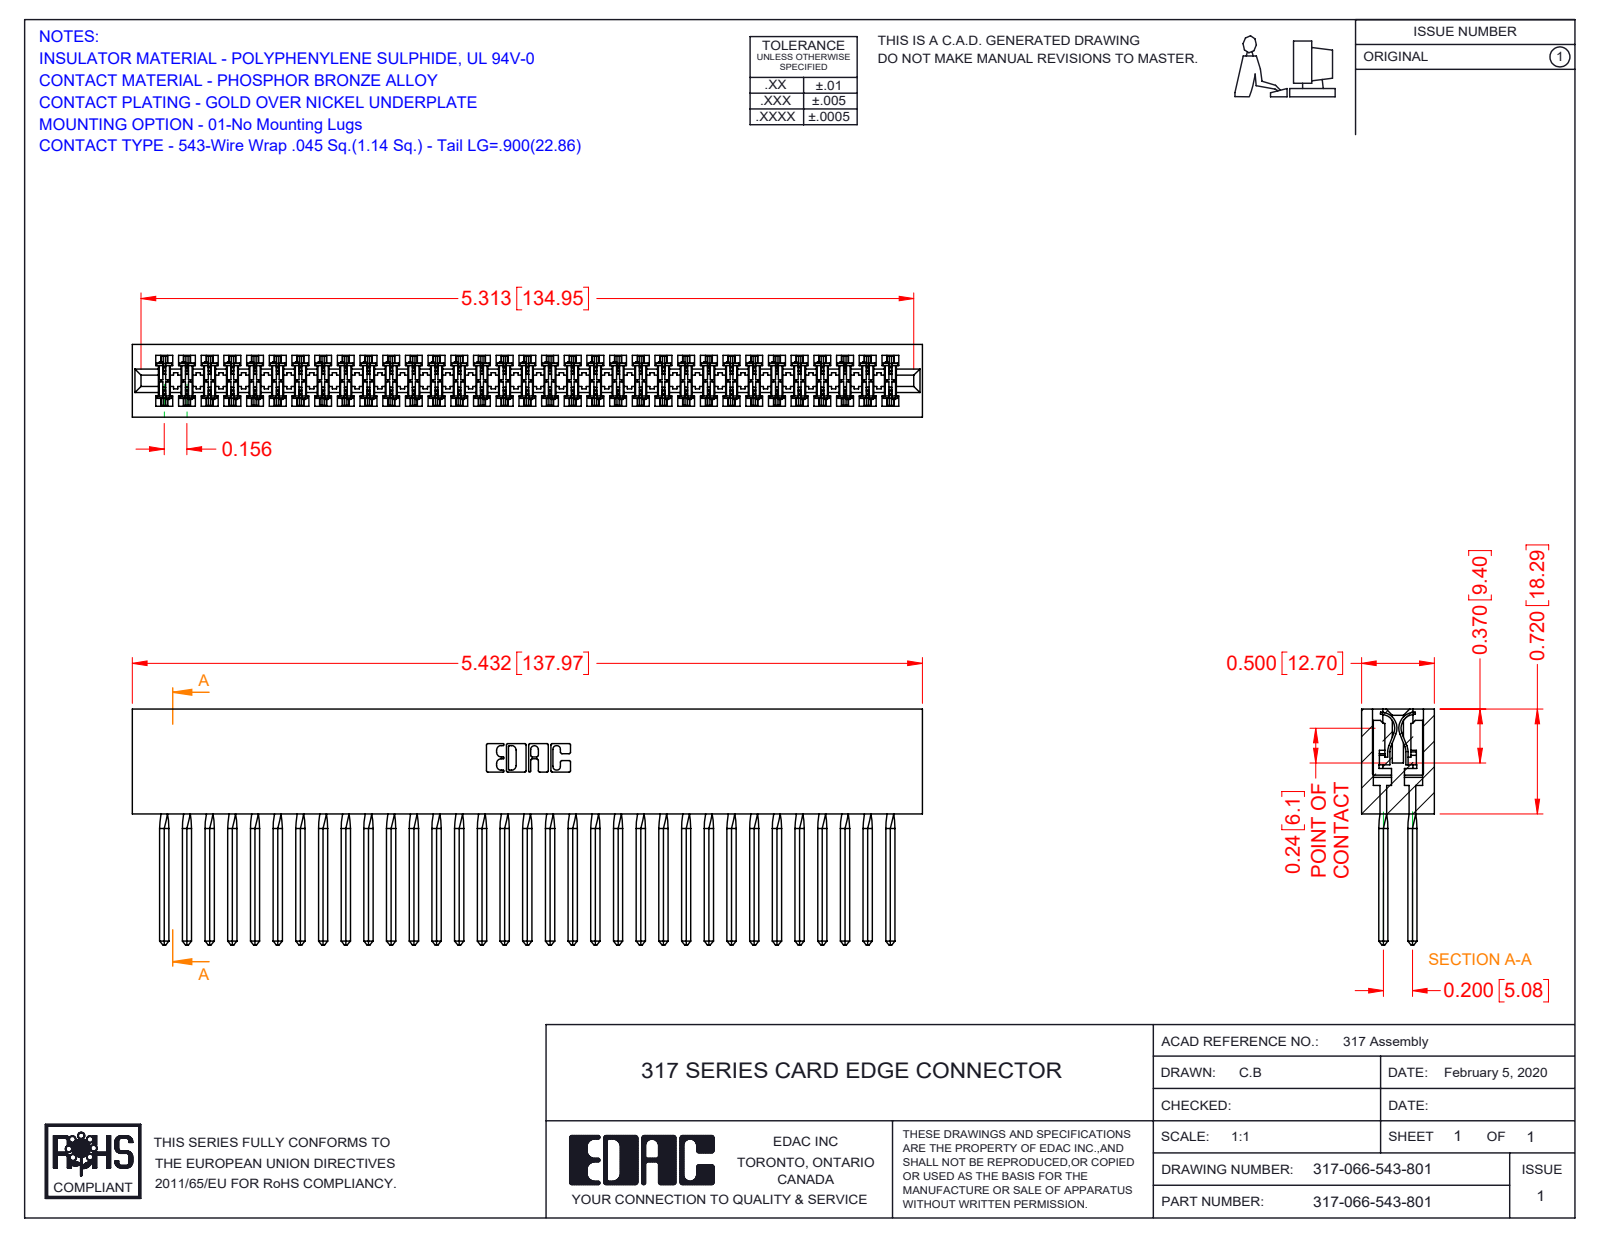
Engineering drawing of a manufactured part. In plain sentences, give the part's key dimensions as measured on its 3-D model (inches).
The part is named "317-066-543-801; 317-290-001_543; 317 Part_Lugless". Its 3-D file was written by "SolidWorks 2016 (CONFIG_CONTROL_DESIGN)". It is 67 solids with 5964 faces: 4868 planar, 832 cylindrical and 264 other. Overall it measures 5.432 by 1.62 by 0.5 inches. Its volume is 1.524 cubic inches and its surface area 58.61 square inches. Partial cylindrical surfaces (rounded edges, fillets, slot ends): 132 of radius 0.015, 22 of radius 0.01, 6 of radius 0.007, 6 of radius 0.031, 3 of radius 0.026, 2 of radius 0.095, 2 of radius 0.1, 2 of radius 0.11. The main face-to-face distances are 0.075, 0.5, 0.425, 0.35, 0.11, 0.195, 0.094, 0.2, 0.115, 0.131.
